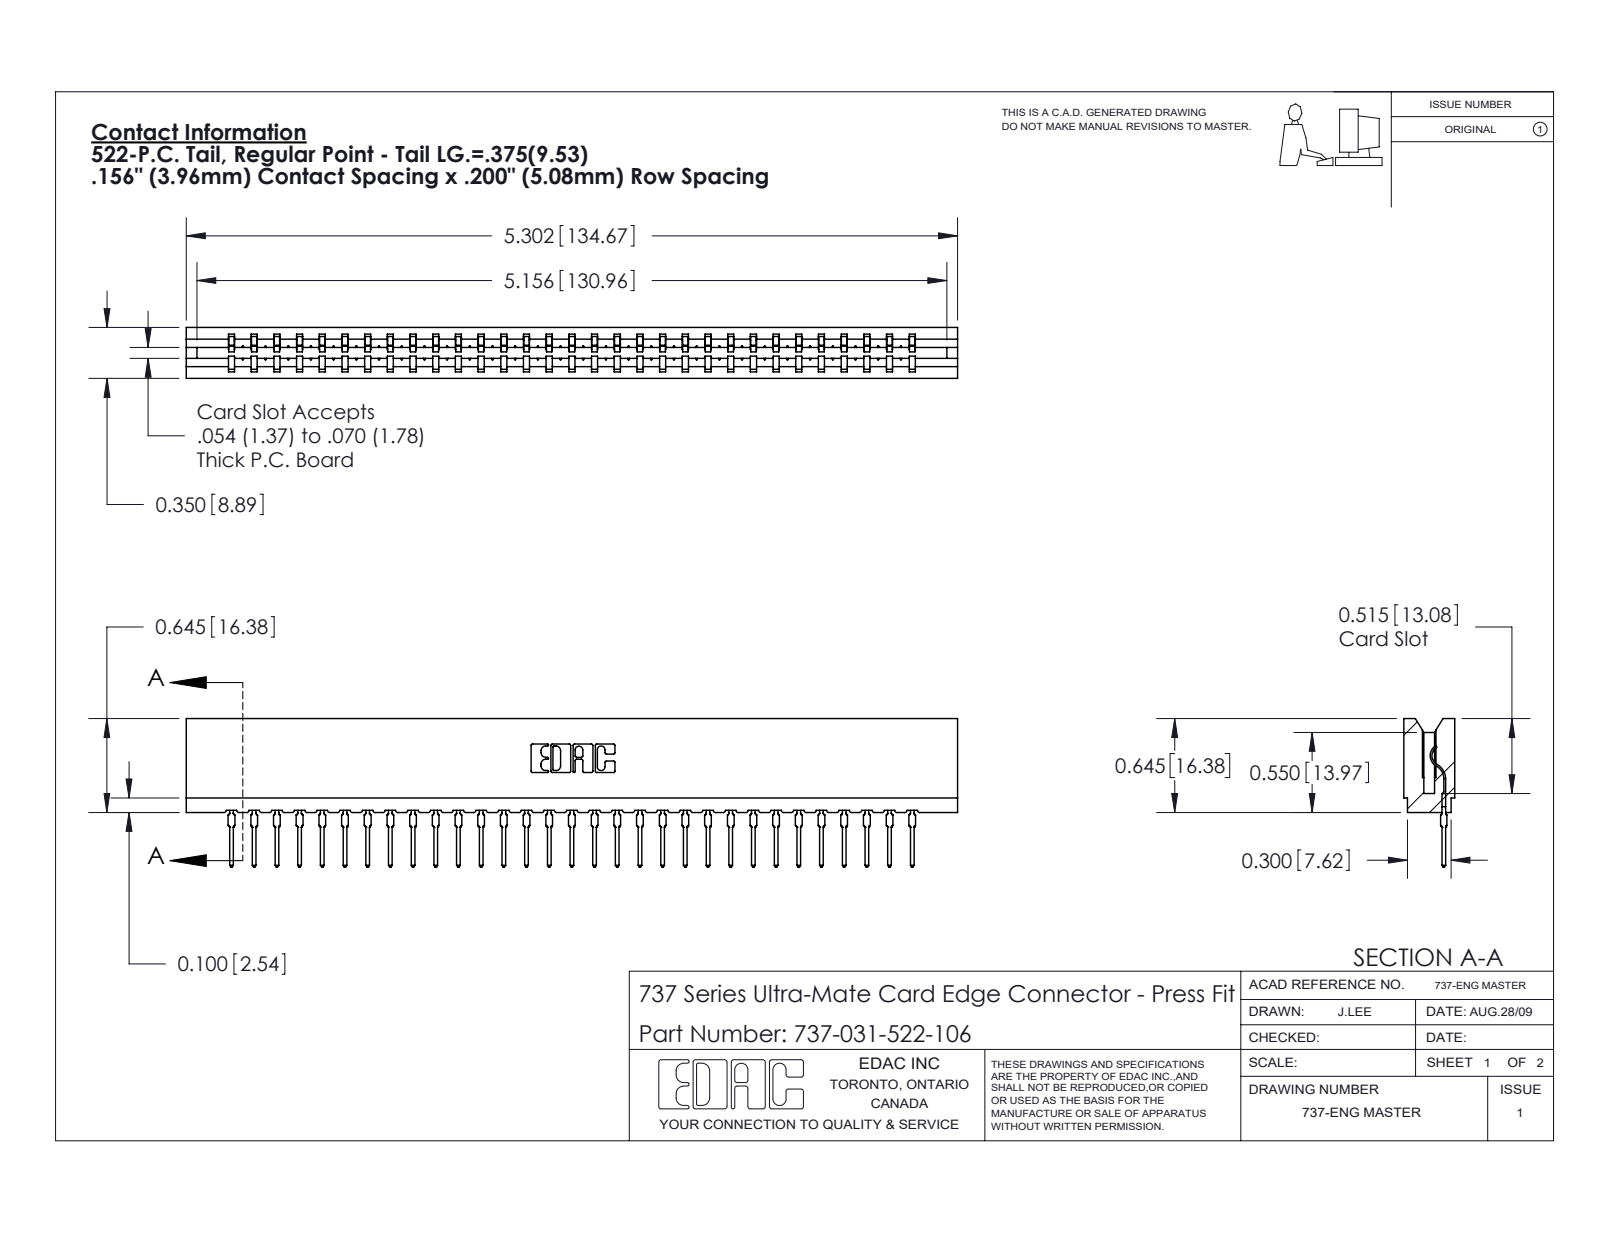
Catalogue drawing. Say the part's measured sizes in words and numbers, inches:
The part is named "737 Part_Insulator Option - 06; 737-031-522-106; 745-292-001_522". Its 3-D file was written by "SolidWorks 2020 (CONFIG_CONTROL_DESIGN)". It is 32 solids with 3598 faces: 2163 planar, 629 cylindrical and 806 other. Overall it measures 5.302 by 1.021 by 0.35 inches. Its volume is 0.799 cubic inches and its surface area 27.08 square inches. Partial cylindrical surfaces (rounded edges, fillets, slot ends): 62 of radius 0.015, 62 of radius 0.021, 22 of radius 0.01, 6 of radius 0.007, 6 of radius 0.031, 4 of radius 0.005, 4 of radius 0.011, 3 of radius 0.026. The main face-to-face distances are 0.138, 0.212, 0.35, 0.074, 0.045, 0.305, 0.093, 0.167, 0.156, 0.624.
